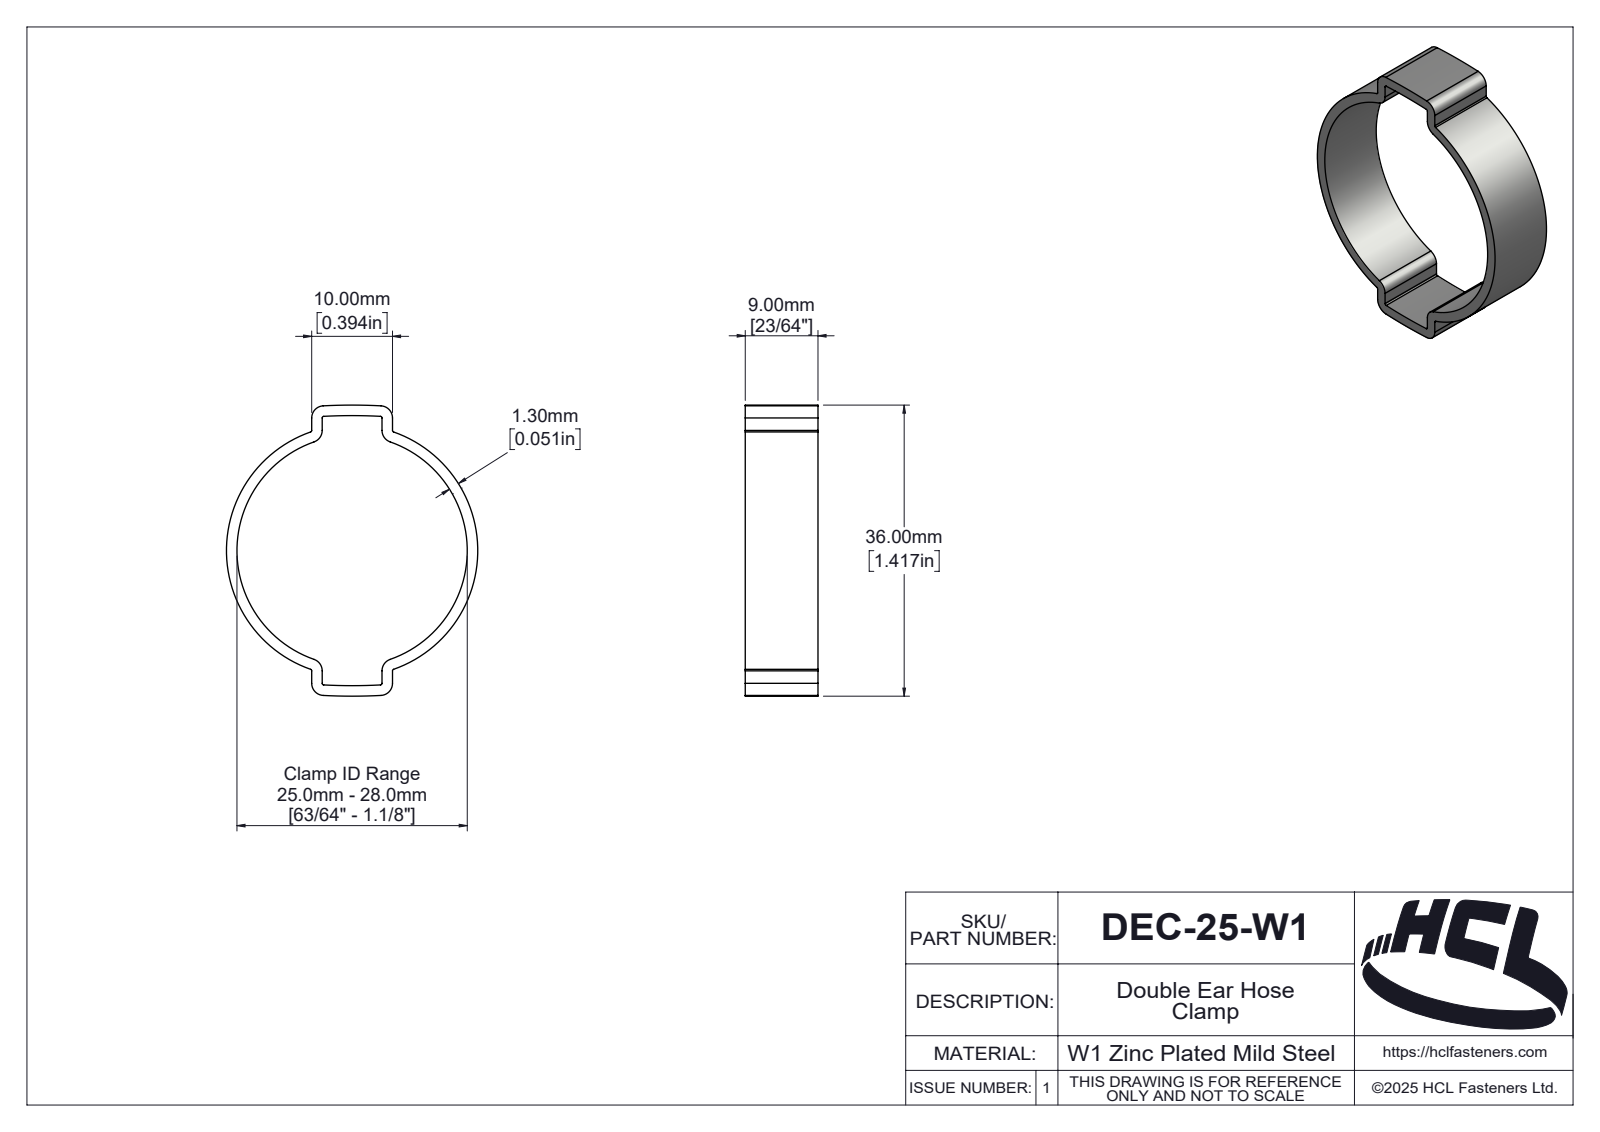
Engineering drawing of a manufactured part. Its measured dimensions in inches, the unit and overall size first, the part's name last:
Units: inches
Overall size (bounding box): 1.417 × 1.224 × 0.354
Partial cylindrical surfaces — rounded edges, fillets, slot ends (radius × count): R0.008 ×8, R0.059 ×8, R2.697 ×2, R2.748 ×2, R0.008 ×1, R0.032 ×1, R0.04 ×1, R0.042 ×1
Main face-to-face distances: 0.354, 0.051, 0.343, 0.394, 0.291, 0.192, 0.141, 0.15, 0.202, 0.186
Volume: 0.074 in³ · Surface area: 3.303 in²
Bodies: 1 solid, 137 faces (12 planar, 67 cylindrical, 58 other)
Part name (STEP PRODUCT): DEC-25-W1
STEP written by: SolidWorks 2025 (AUTOMOTIVE_DESIGN)
